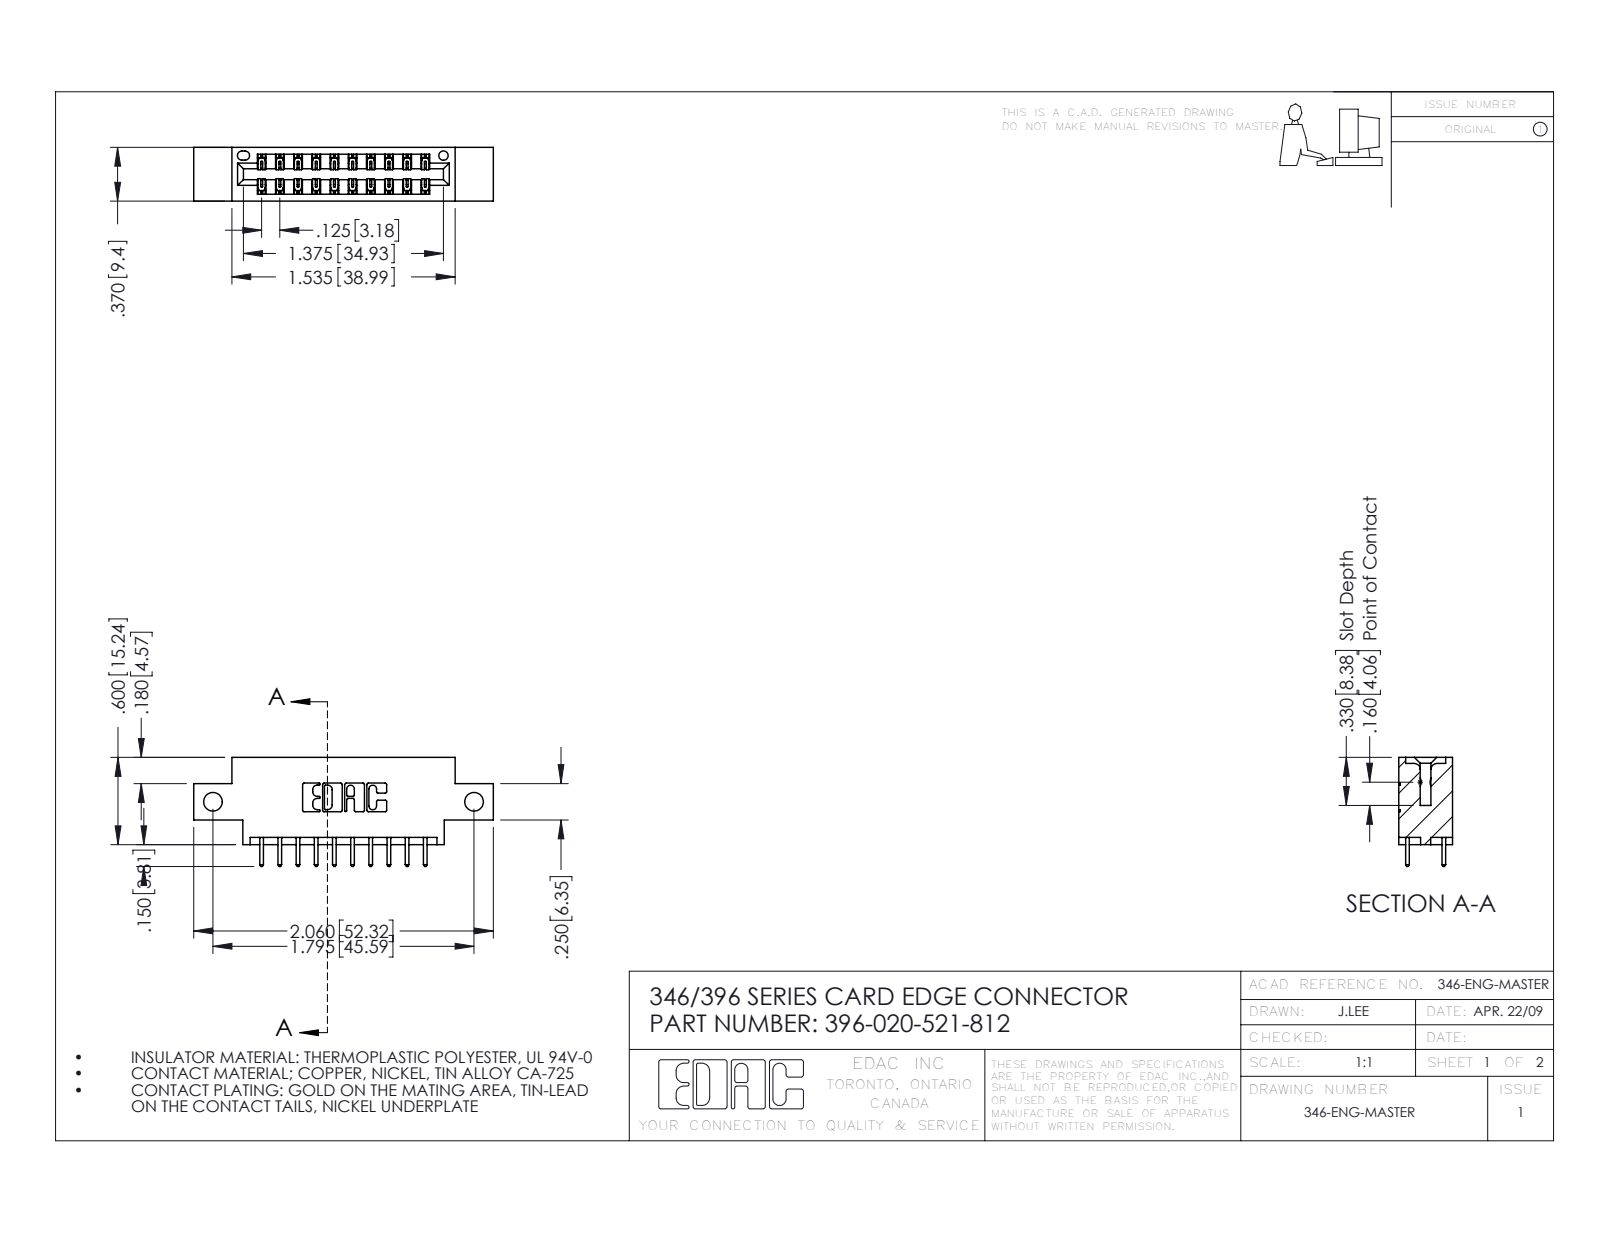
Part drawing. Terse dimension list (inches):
name: 345-292-001_345-293-121; 396-020-521-812; 346 Part_0.170 Offset - Side Mount
written by: SolidWorks 2016 (CONFIG_CONTROL_DESIGN)
unit: in
bodies: 21 solids, 1166 faces (780 planar, 386 cylindrical, 0 other)
size: 2.06 × 0.75 × 0.37
volume: 0.281 in³; area: 9.009 in²
holes: 2× ⌀0.128, 1× ⌀0.064
rounds: 30× R0.006, 22× R0.01, 20× R0.01, 6× R0.007, 6× R0.031, 3× R0.026, 2× R0.014, 2× R0.022
face distances: 0.25, 0.048, 0.322, 0.37, 0.072, 0.298, 0.025, 0.275, 0.148, 0.222
hole spacings: 1.795
